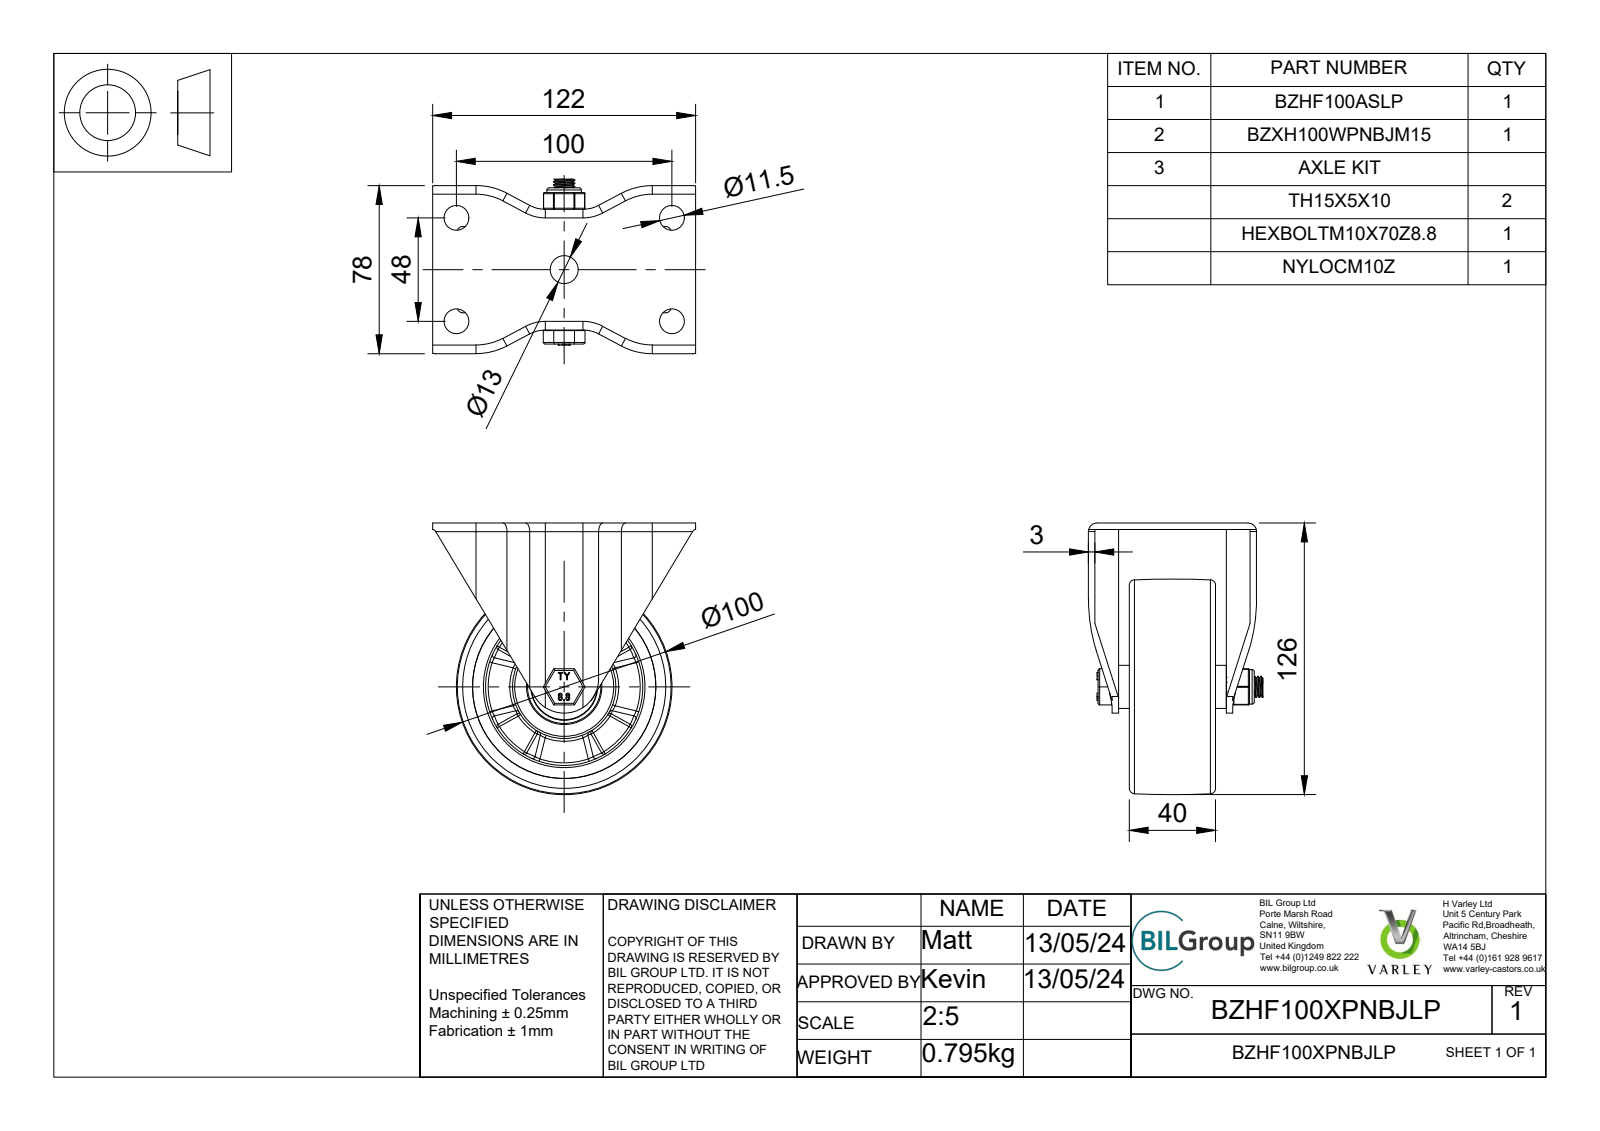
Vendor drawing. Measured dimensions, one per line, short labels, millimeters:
name: BZHF100XPNBJLP v3; BZHF100ASLP - 50 v1; ZINC PLATED PRESSED STEEL BRACKET; BZXH100WPNBJM15 v1 (+7 more)
written by: Autodesk Translation Framework v12.20.1.177 (AUTOMOTIVE_DESIGN)
unit: mm
bodies: 35 solids, 1172 faces (396 planar, 197 cylindrical, 579 other)
size: 126 × 122 × 81
volume: 289 976 mm³; area: 136 999 mm²
holes: 4× ⌀11.5, 1× ⌀10, 1× ⌀10.5, 1× ⌀10.8, 1× ⌀12, 1× ⌀13, 1× ⌀15, 1× ⌀22.5, 1× ⌀30, 1× ⌀31, 1× ⌀32, 1× ⌀35
bosses: 1× ⌀48, 1× ⌀30.5, 1× ⌀23, 1× ⌀22, 1× ⌀20, 1× ⌀18, 1× ⌀16, 1× ⌀14.75
rounds: 18× R0.5, 8× R4, 6× R0.75, 4× R15.5, 4× R30.5, 2× R2, 1× R12, 1× R13.75
face distances: 3, 5, 45, 40, 8, 11, 48, 56, 64, 16
hole spacings: 55.46, 48, 100, 110.92
